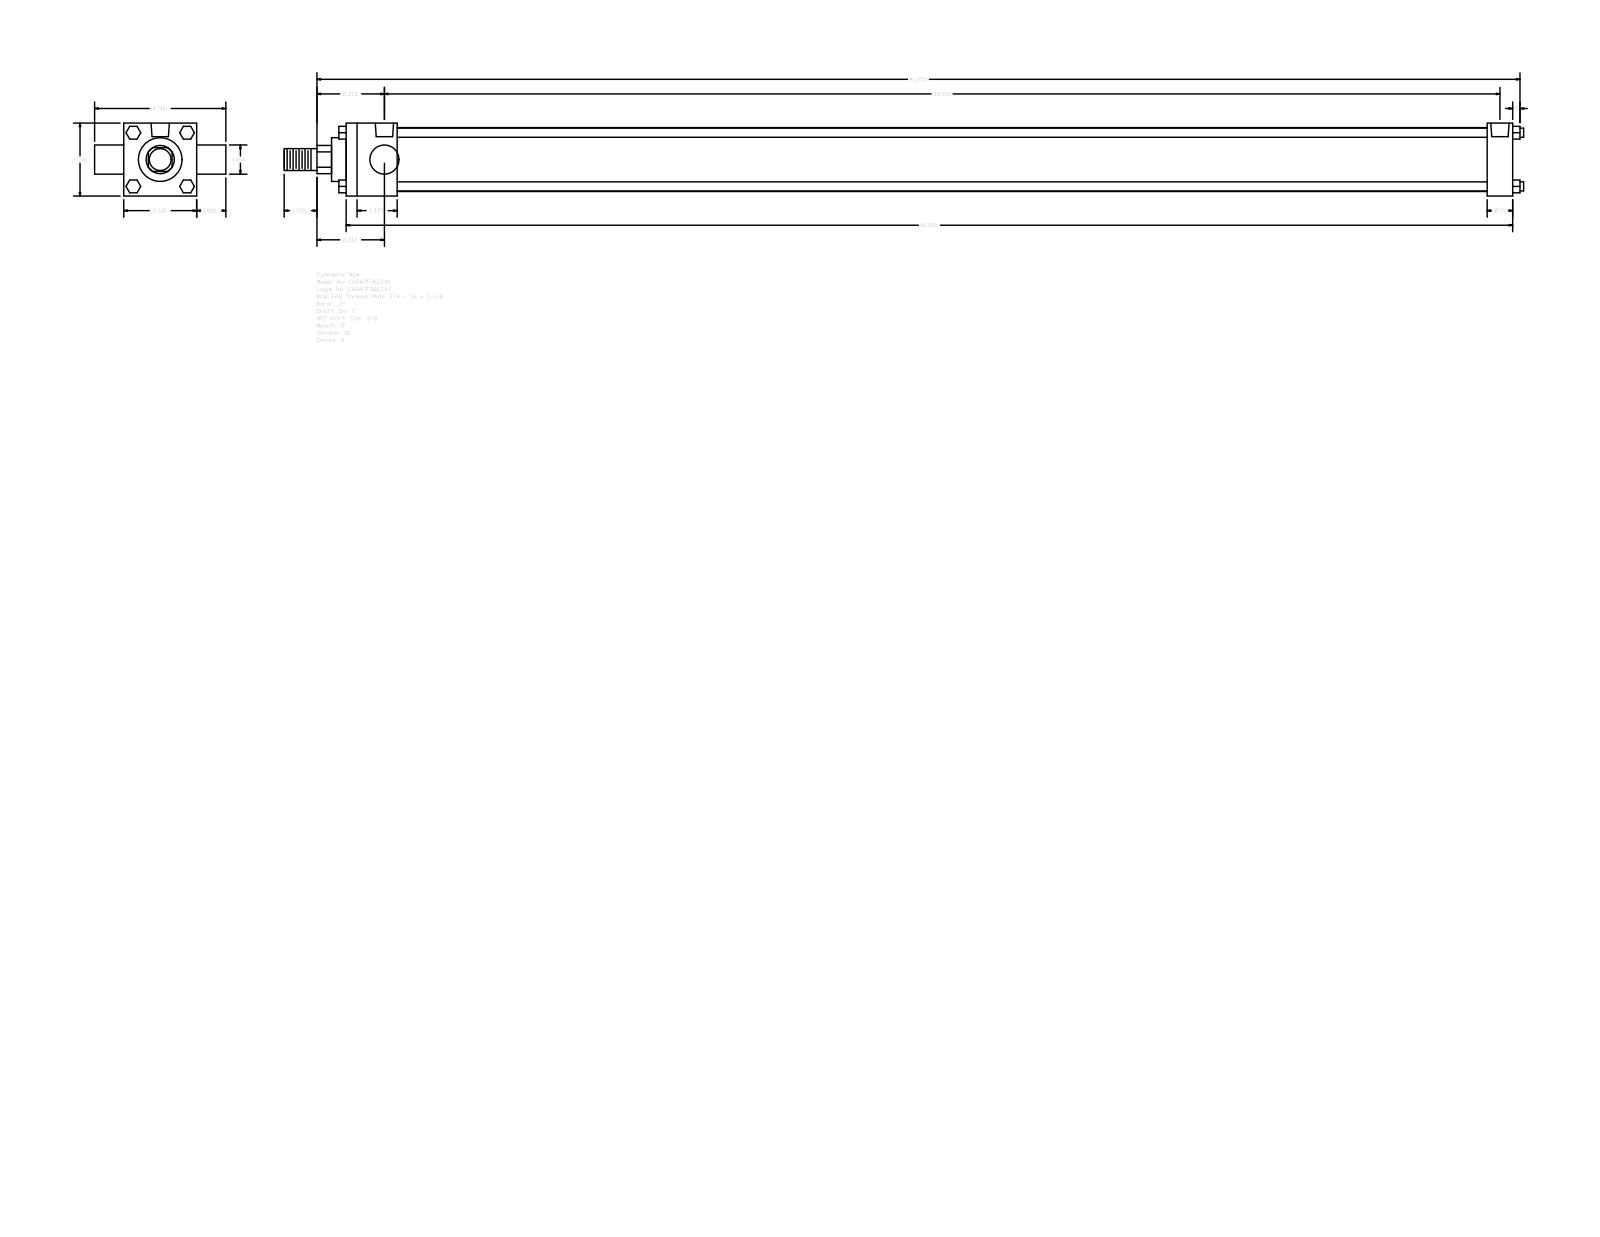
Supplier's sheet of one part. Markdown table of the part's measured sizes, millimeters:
| quantity | value |
| --- | --- |
| part name | A_TF__0200_1 |
| STEP written by | GSSL Pune (CONFIG_CONTROL_DESIGN) |
| units | millimeters |
| bodies | 0 solids, 120 faces (92 planar, 28 cylindrical, 0 other) |
| overall size | 1079.5 × 114.3 × 63.5 |
| round holes (diameter × count) | 5.56 × 3, 15.93 × 2 |
| round bosses / shafts (diameter × count) | 7.94 × 4, 25.4 × 2, 55.63 × 1, 38.1 × 1, 19.05 × 1 |
| partial cylindrical surfaces (radius × count) | 12.29 × 1 |
| main face-to-face distances | 63.5, 1016, 44.45, 993.77, 949.32, 971.55, 22.23, 25.4, 88.9, 1028.7 |
| hole center spacings | 1.59, 3.98, 965.98, 967.57, 969.96, 971.55 |
